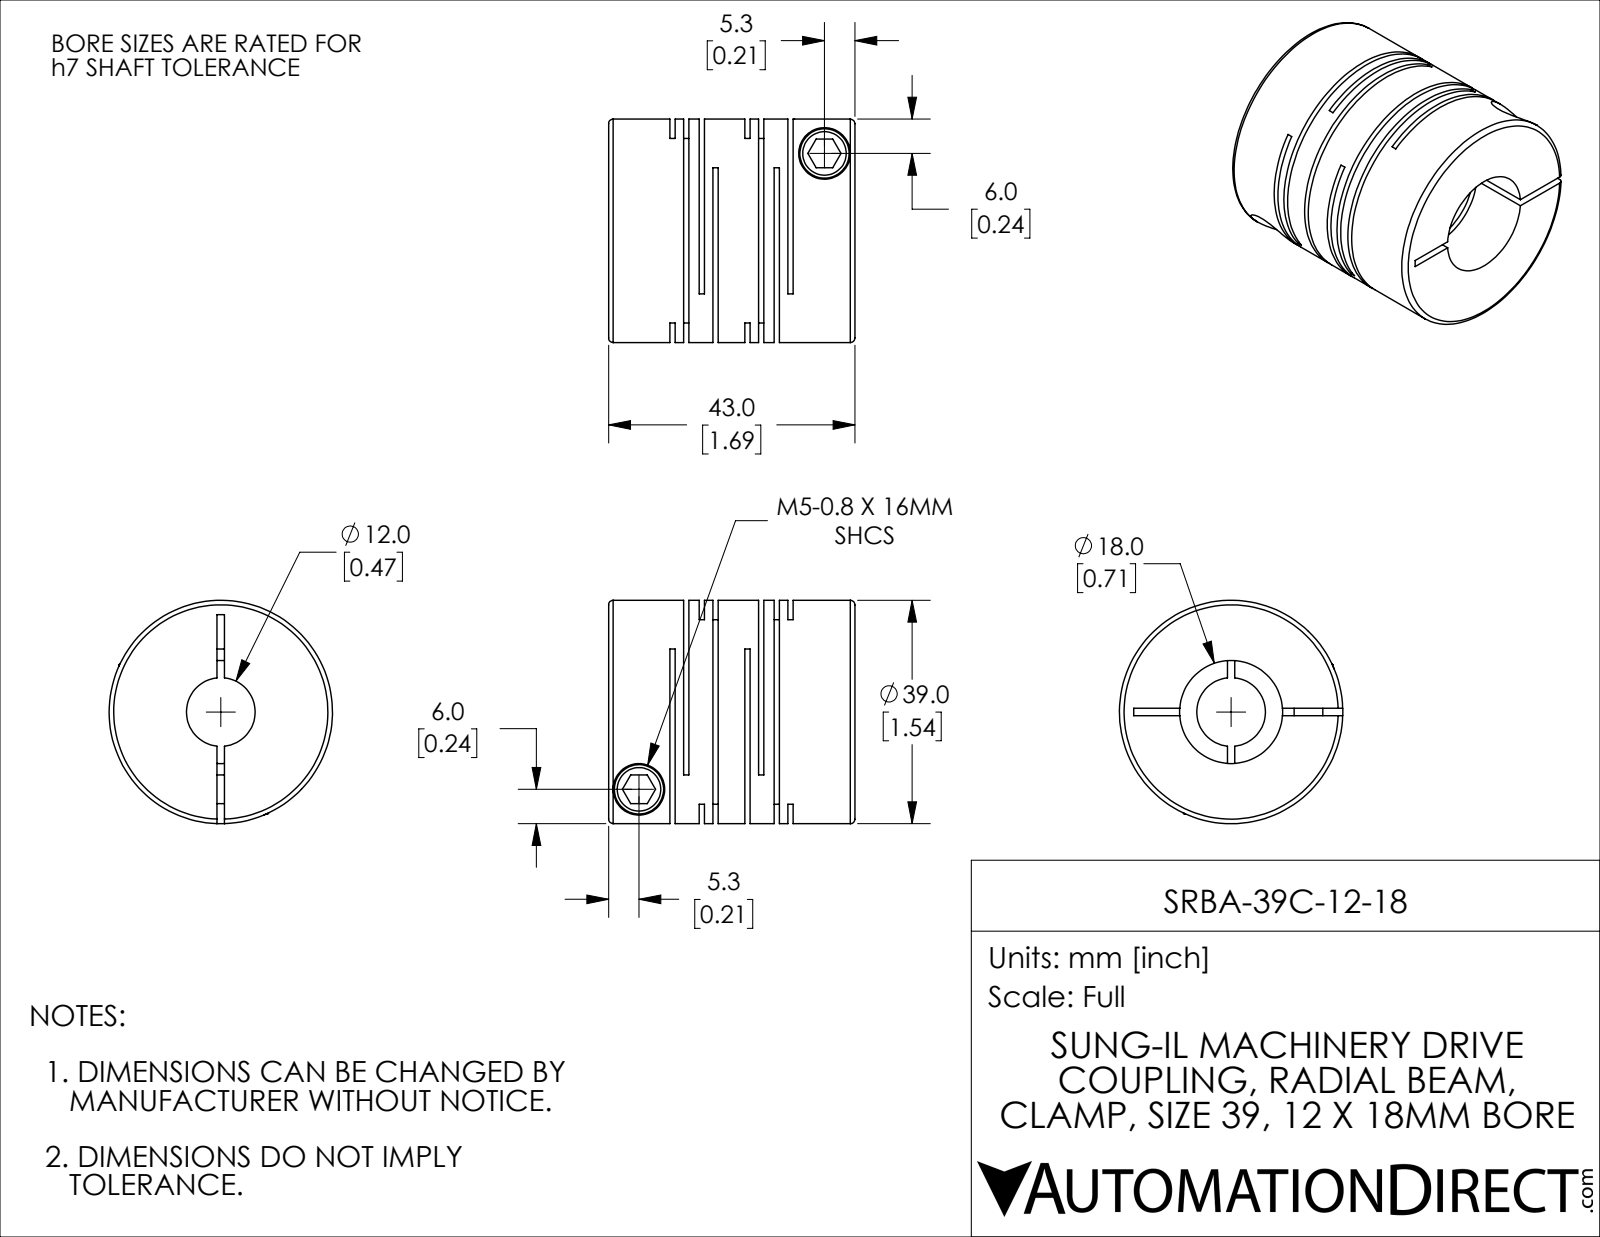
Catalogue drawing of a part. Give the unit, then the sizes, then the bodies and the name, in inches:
Units: inches
Overall size (bounding box): 1.693 × 1.535 × 1.535
Round holes (diameter × count): ⌀0.197 ×2, ⌀0.354 ×2, ⌀0.472 ×1, ⌀0.709 ×1
Round bosses / shafts (diameter × count): ⌀0.339 ×2, ⌀1.535 ×1
Main face-to-face distances: 0.516, 0.036, 0.094, 0.201, 0.421, 0.552, 0.717, 0.131, 0.058, 0.61
Volume: 2.131 in³ · Surface area: 34.6 in²
Bodies: 1 solid, 114 faces (60 planar, 42 cylindrical, 12 other)
Part name (STEP PRODUCT): SRBA-39C-12-18
STEP written by: SolidWorks 2021 (CONFIG_CONTROL_DESIGN)
